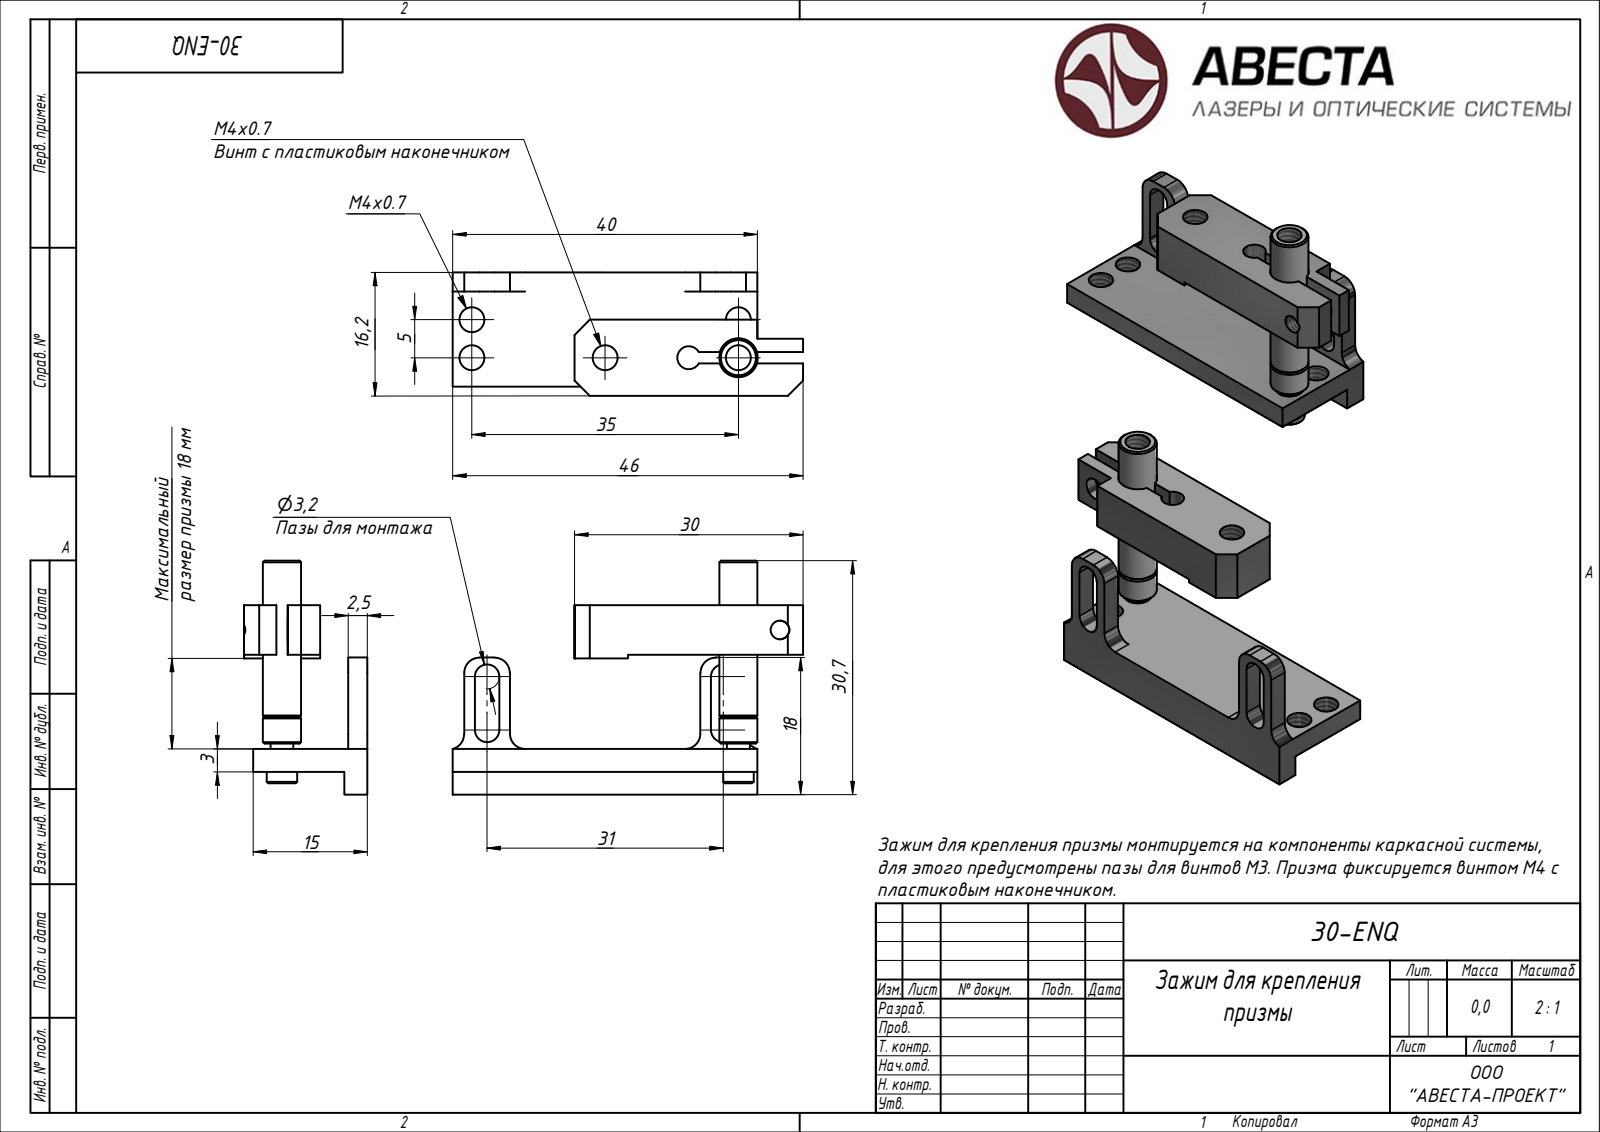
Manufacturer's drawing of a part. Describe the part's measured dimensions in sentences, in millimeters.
Its 3-D file was written by "ST-DEVELOPER v15 (AUTOMOTIVE_DESIGN)". It is 3 solids with 100 faces: 43 planar, 0 cylindrical and 57 other. Overall it measures 46.04 by 30.7 by 16.31 millimeters. Its volume is 4 225 cubic millimeters and its surface area 4 118 square millimeters. The main face-to-face distances are 3, 18.87, 21.87, 6, 15.37, 12.37, 6.5, 9.99, 0.5, 15.
